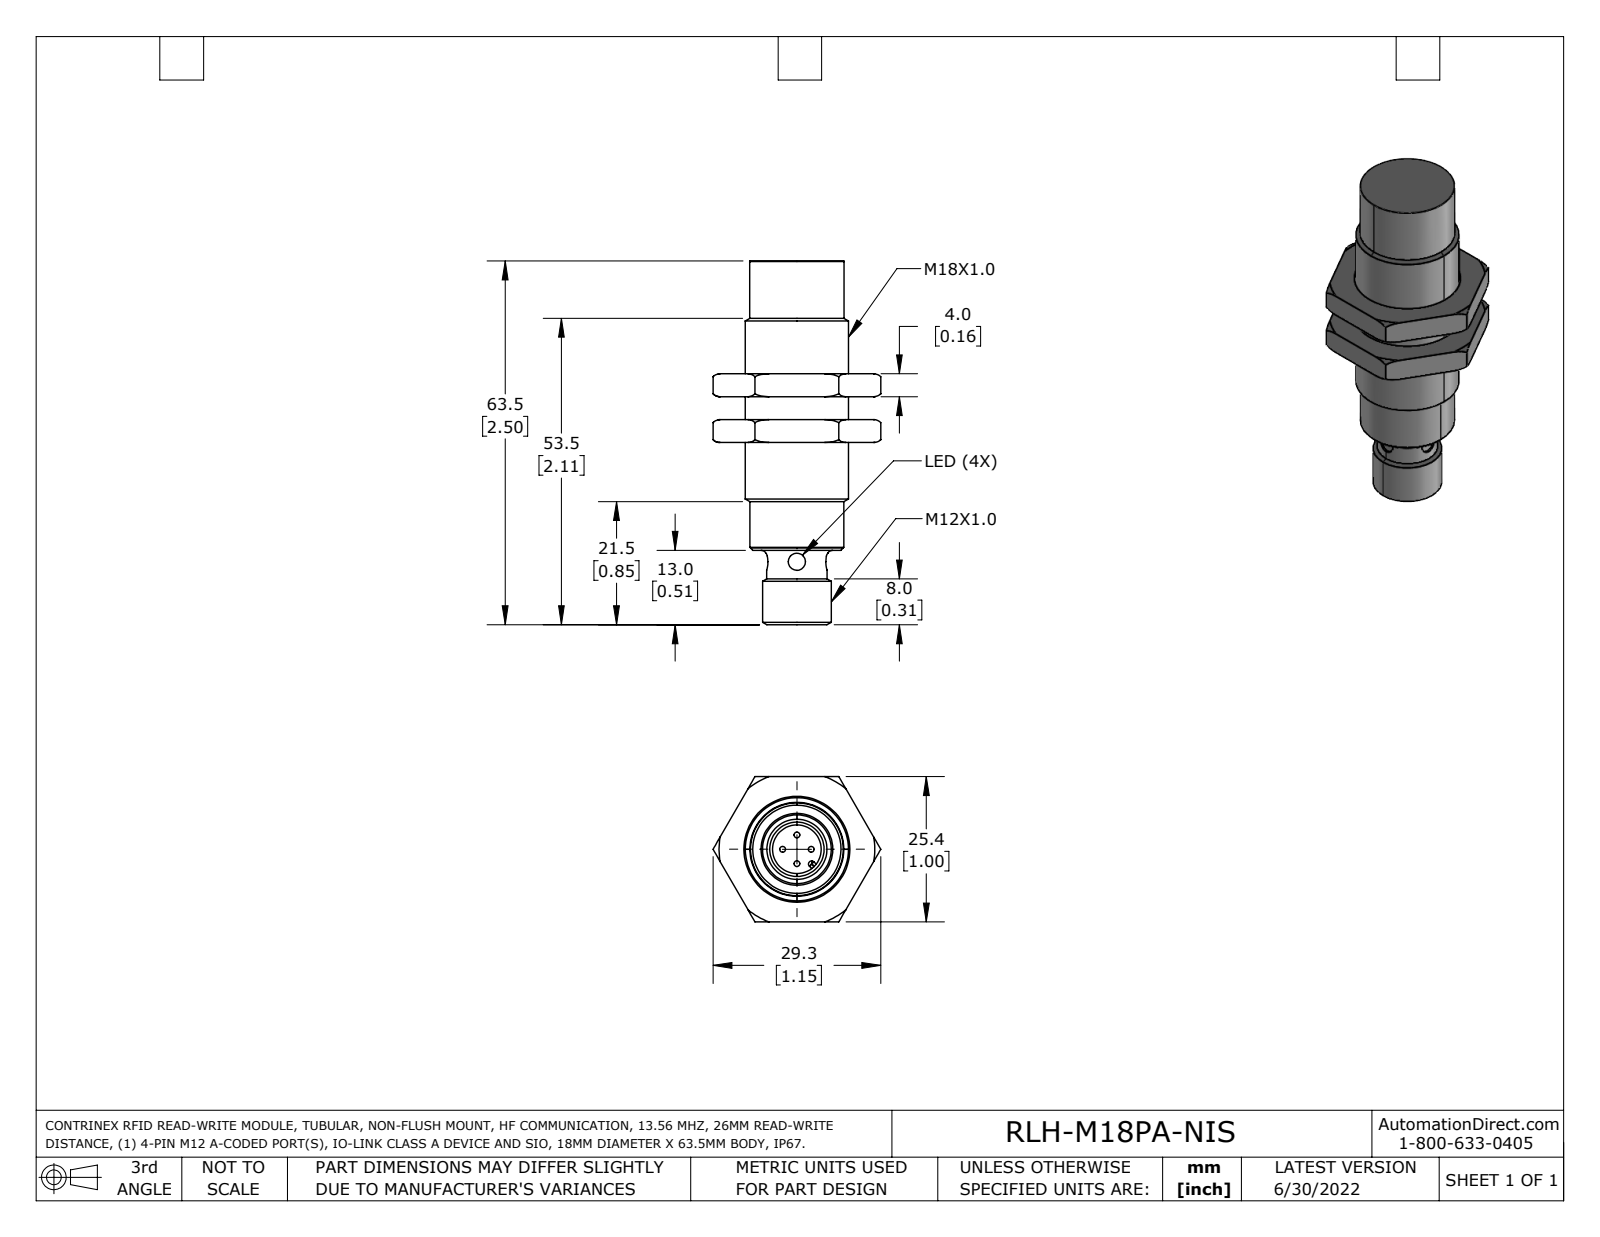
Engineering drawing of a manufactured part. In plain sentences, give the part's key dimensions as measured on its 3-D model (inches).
The part is named "RLH-M18PA-NIS". Its 3-D file was written by "SolidWorks 2021 (AUTOMOTIVE_DESIGN)". It is 3 solids with 127 faces: 25 planar, 40 cylindrical and 62 other. Overall it measures 2.5 by 1.153 by 0.998 inches. Its volume is 0.925 cubic inches and its surface area 9.858 square inches. Round holes: 2 of diameter 0.118, 1 of diameter 0.335, 1 of diameter 0.689. Round bosses or shafts: 4 of diameter 0.039, 1 of diameter 0.709, 1 of diameter 0.65, 1 of diameter 0.646, 1 of diameter 0.638, 1 of diameter 0.472, 1 of diameter 0.415. Partial cylindrical surfaces (rounded edges, fillets, slot ends): 2 of radius 0.02, 1 of radius 0.022. The main face-to-face distances are 0.157, 0.315, 0.998, 0.472, 0.775, 0.933, 1.09, 1.248, 1.213, 1.988.
